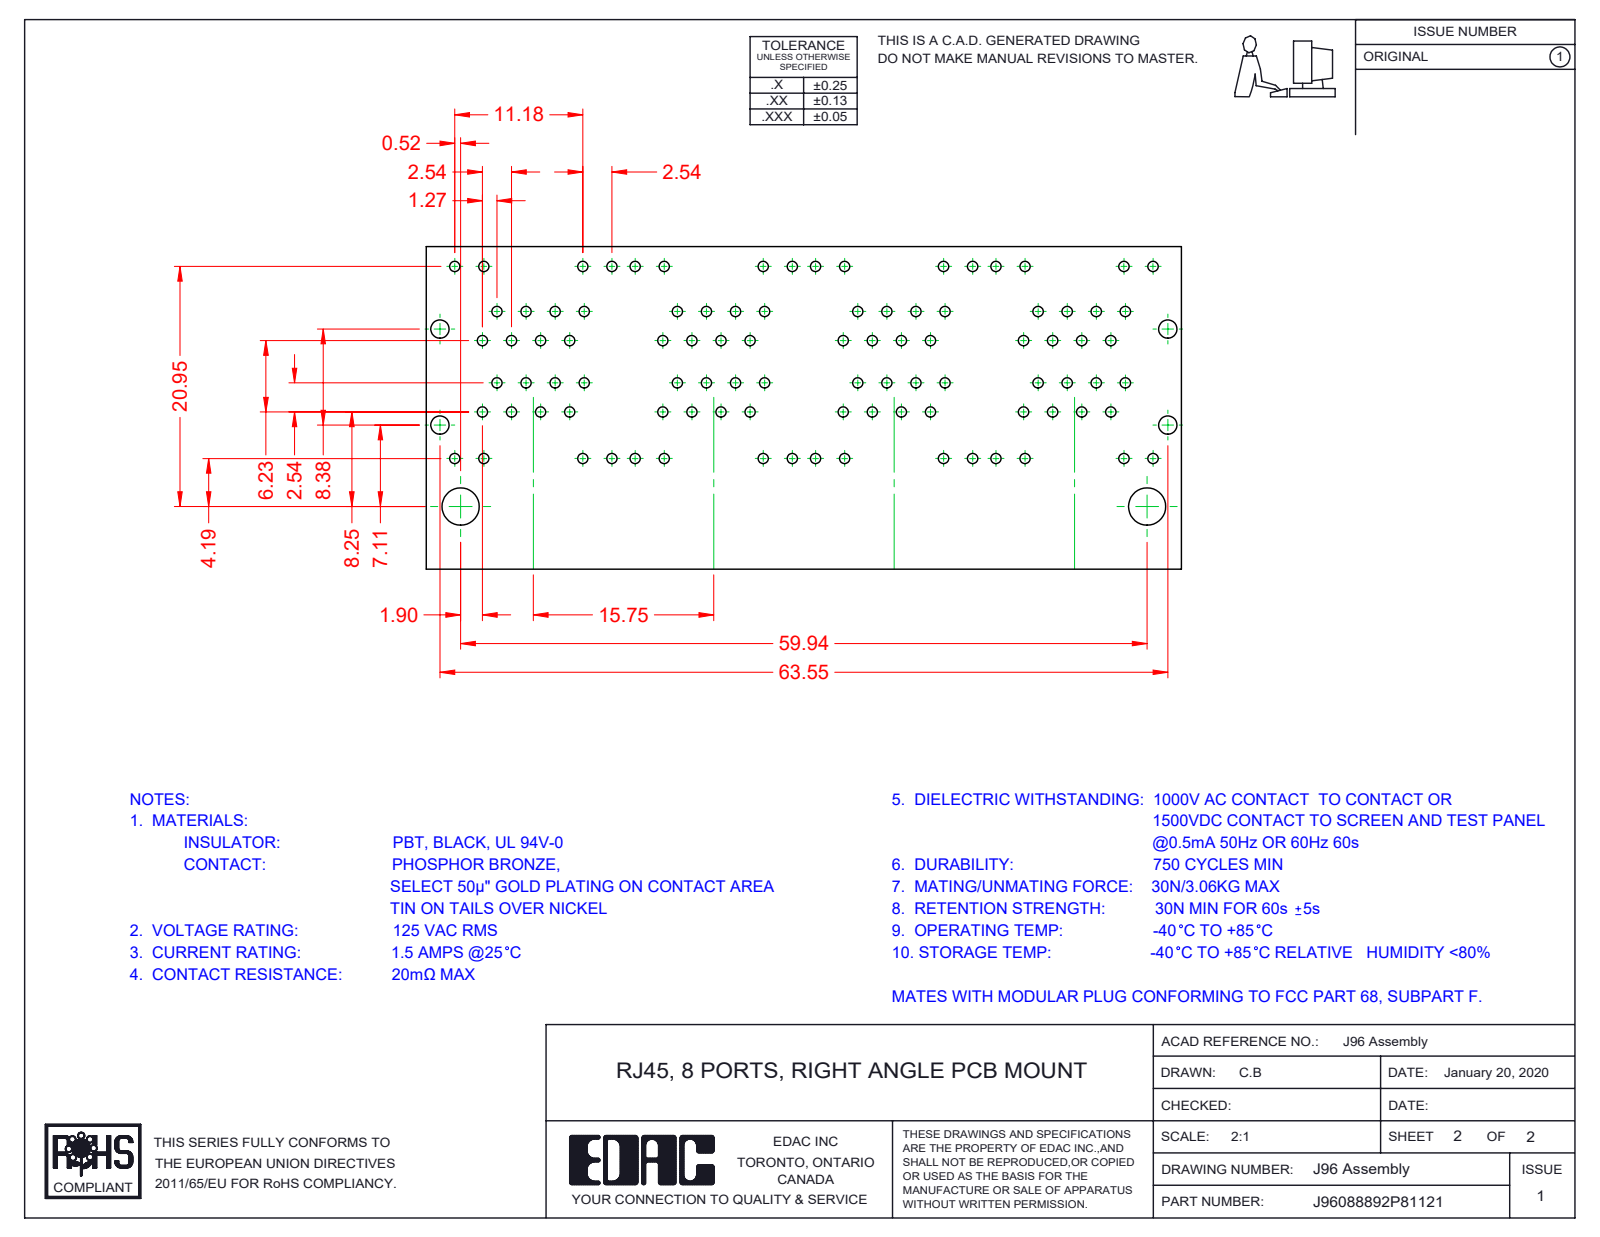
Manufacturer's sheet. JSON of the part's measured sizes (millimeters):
{"part_name": "96 LED LH Upper_8-Red-Yellow; 96 Contacts Lower; 96 LED RH Lower_1-Yellow; 96 LED RH Upper_1-Yellow (+8 more)", "step_written_by": "SolidWorks 2016 (CONFIG_CONTROL_DESIGN)", "units": "millimeters", "bodies": {"solids": 96, "faces": 7658, "planar": 6069, "cylindrical": 1323, "other": 266}, "overall_size": [64.05, 29.58, 28.68], "volume_mm3": 24160, "surface_area_mm2": 63658, "round_holes": [[1.7, 3]], "round_bosses_or_shafts": [[1.68, 3]], "partial_cylinders_radius": [[0.25, 124], [0.35, 73], [1, 72], [0.5, 49], [0.91, 32], [0.2, 21], [0.7, 11], [0.22, 8]], "face_to_face_distances": [15.75, 0.35, 9.95, 1.17, 1.6, 0.54, 9.98, 10.18, 12.67, 3.37], "hole_center_spacings": [15.75, 31.5]}
